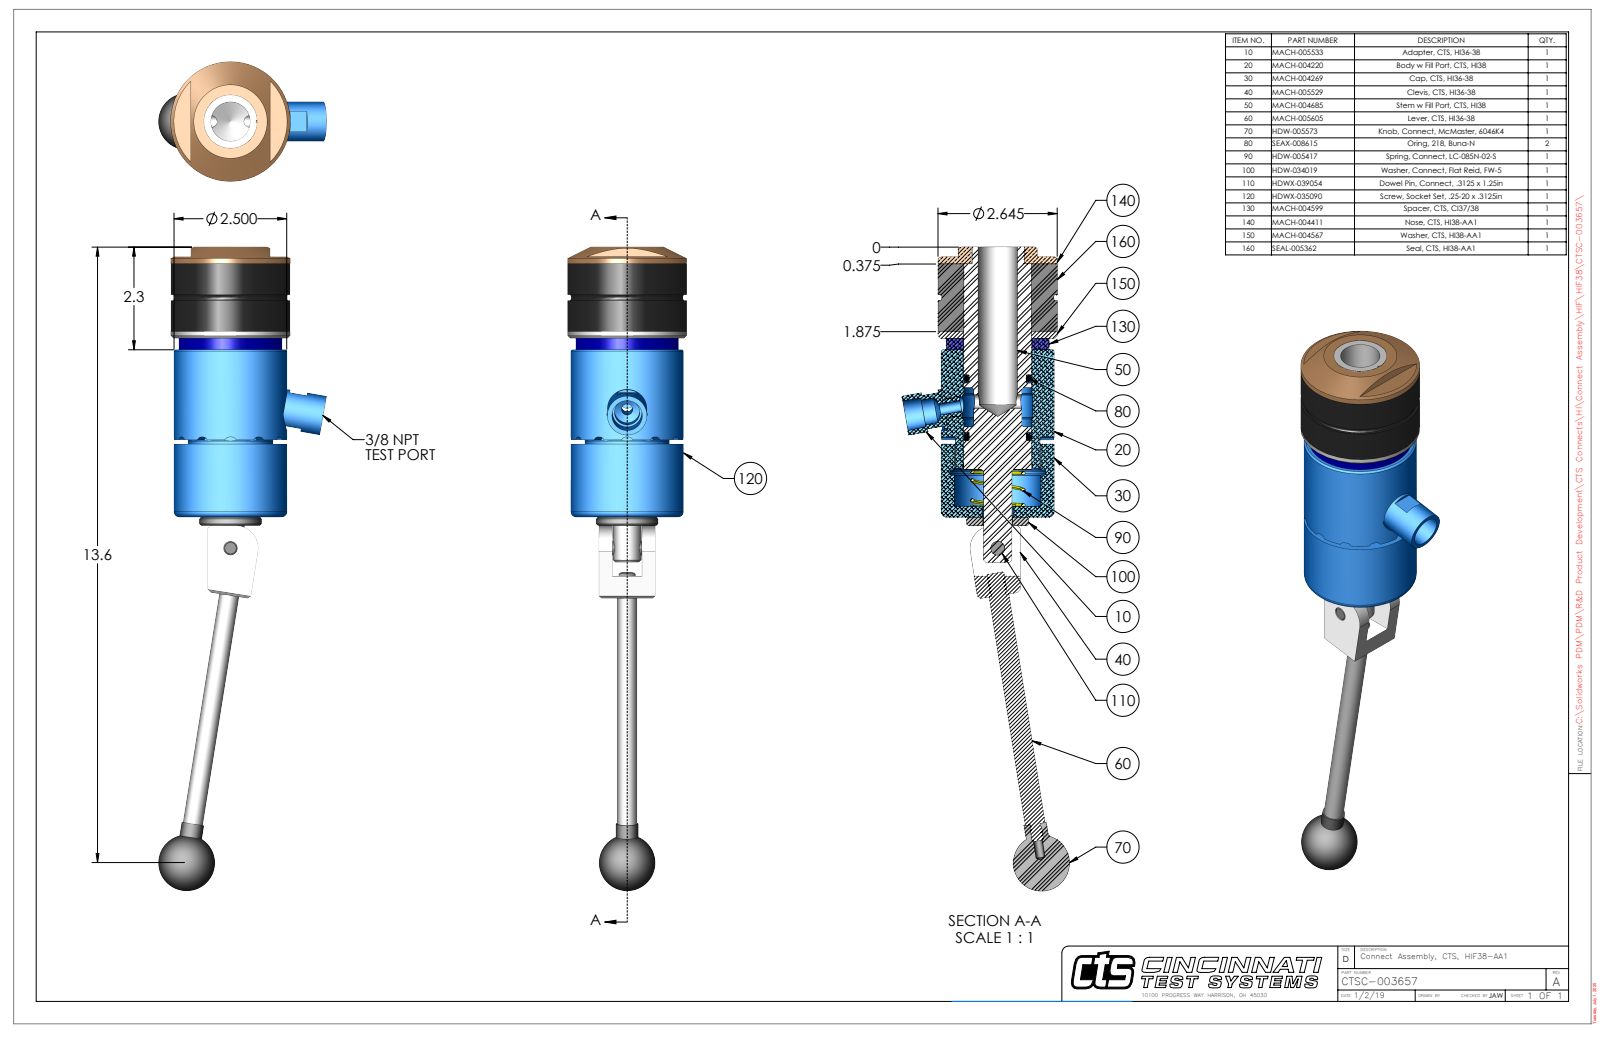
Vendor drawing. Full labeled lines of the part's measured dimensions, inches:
Part name (STEP PRODUCT): CTSC-003657
STEP written by: SolidWorks 2023 (AUTOMOTIVE_DESIGN)
Units: inches
Bodies: 10 solids, 309 faces (110 planar, 126 cylindrical, 73 other)
Overall size (bounding box): 14.275 × 3.716 × 2.645
Volume: 31.19 in³ · Surface area: 156.2 in²
Round holes (diameter × count): ⌀0.201 ×2, ⌀0.15 ×1, ⌀0.25 ×1, ⌀0.311 ×1, ⌀0.312 ×1, ⌀0.313 ×1, ⌀0.314 ×1, ⌀0.562 ×1, ⌀0.656 ×1, ⌀0.696 ×1, ⌀0.875 ×1, ⌀1.172 ×1
Round bosses / shafts (diameter × count): ⌀2.645 ×1, ⌀2.645 ×1, ⌀2.5 ×1, ⌀2.281 ×1, ⌀1.875 ×1, ⌀1.5 ×1, ⌀1.498 ×1, ⌀1.38 ×1
Partial cylindrical surfaces — rounded edges, fillets, slot ends (radius × count): R0.12 ×12, R0.029 ×2, R0.19 ×1, R0.195 ×1, R0.47 ×1, R0.476 ×1, R0.5 ×1, R1.198 ×1
Main face-to-face distances: 1.5, 0.152, 1.652, 0.25, 0.402, 1.902, 3.713, 3.963, 4.115, 5.615
Hole centre spacings: 0.74, 2.118, 2.858
